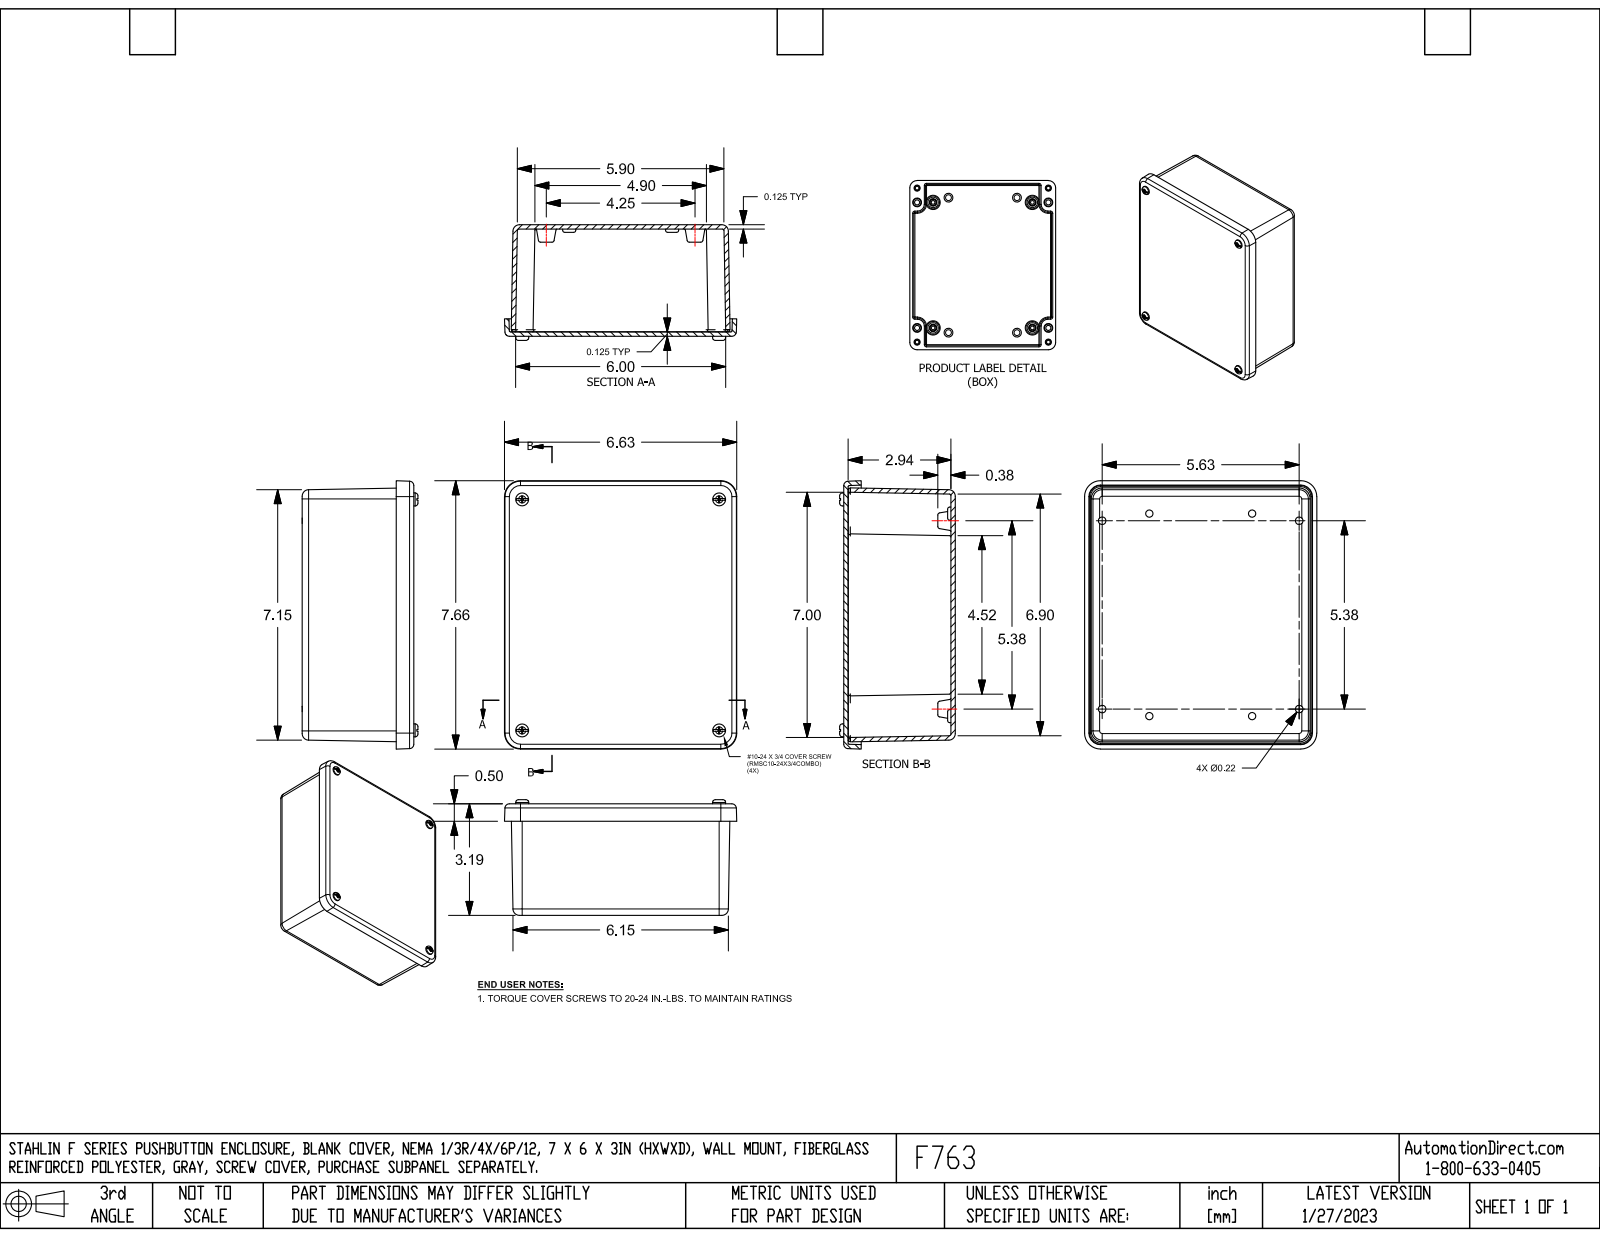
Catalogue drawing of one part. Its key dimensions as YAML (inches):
part_name: "CO763"
step_written_by: "SolidWorks 2018 (AUTOMOTIVE_DESIGN)"
units: inches
bodies: {solids: 15, faces: 356, planar: 148, cylindrical: 112, other: 96}
overall_size: [7.66, 6.633, 3.306]
volume: 28.12
surface_area: 392.6
round_holes:
  - {diameter: 0.159, count: 8}
  - {diameter: 0.219, count: 8}
  - {diameter: 0.21, count: 4}
  - {diameter: 0.25, count: 4}
  - {diameter: 0.281, count: 4}
round_bosses_or_shafts:
  - {diameter: 0.27, count: 8}
  - {diameter: 0.375, count: 4}
  - {diameter: 0.371, count: 4}
  - {diameter: 0.177, count: 4}
partial_cylinders:
  - {radius: 0.031, count: 20}
  - {radius: 0.012, count: 16}
  - {radius: 0.044, count: 8}
  - {radius: 0.125, count: 4}
  - {radius: 0.187, count: 4}
face_to_face_distances: [0.125, 0.125, 3.063, 3.187, 2.937, 3.062, 0.5, 0.625, 0.063, 0.187]
hole_center_spacings: [0.609, 0.687, 0.688, 0.919, 1.359, 1.404, 3.6, 4.286]
